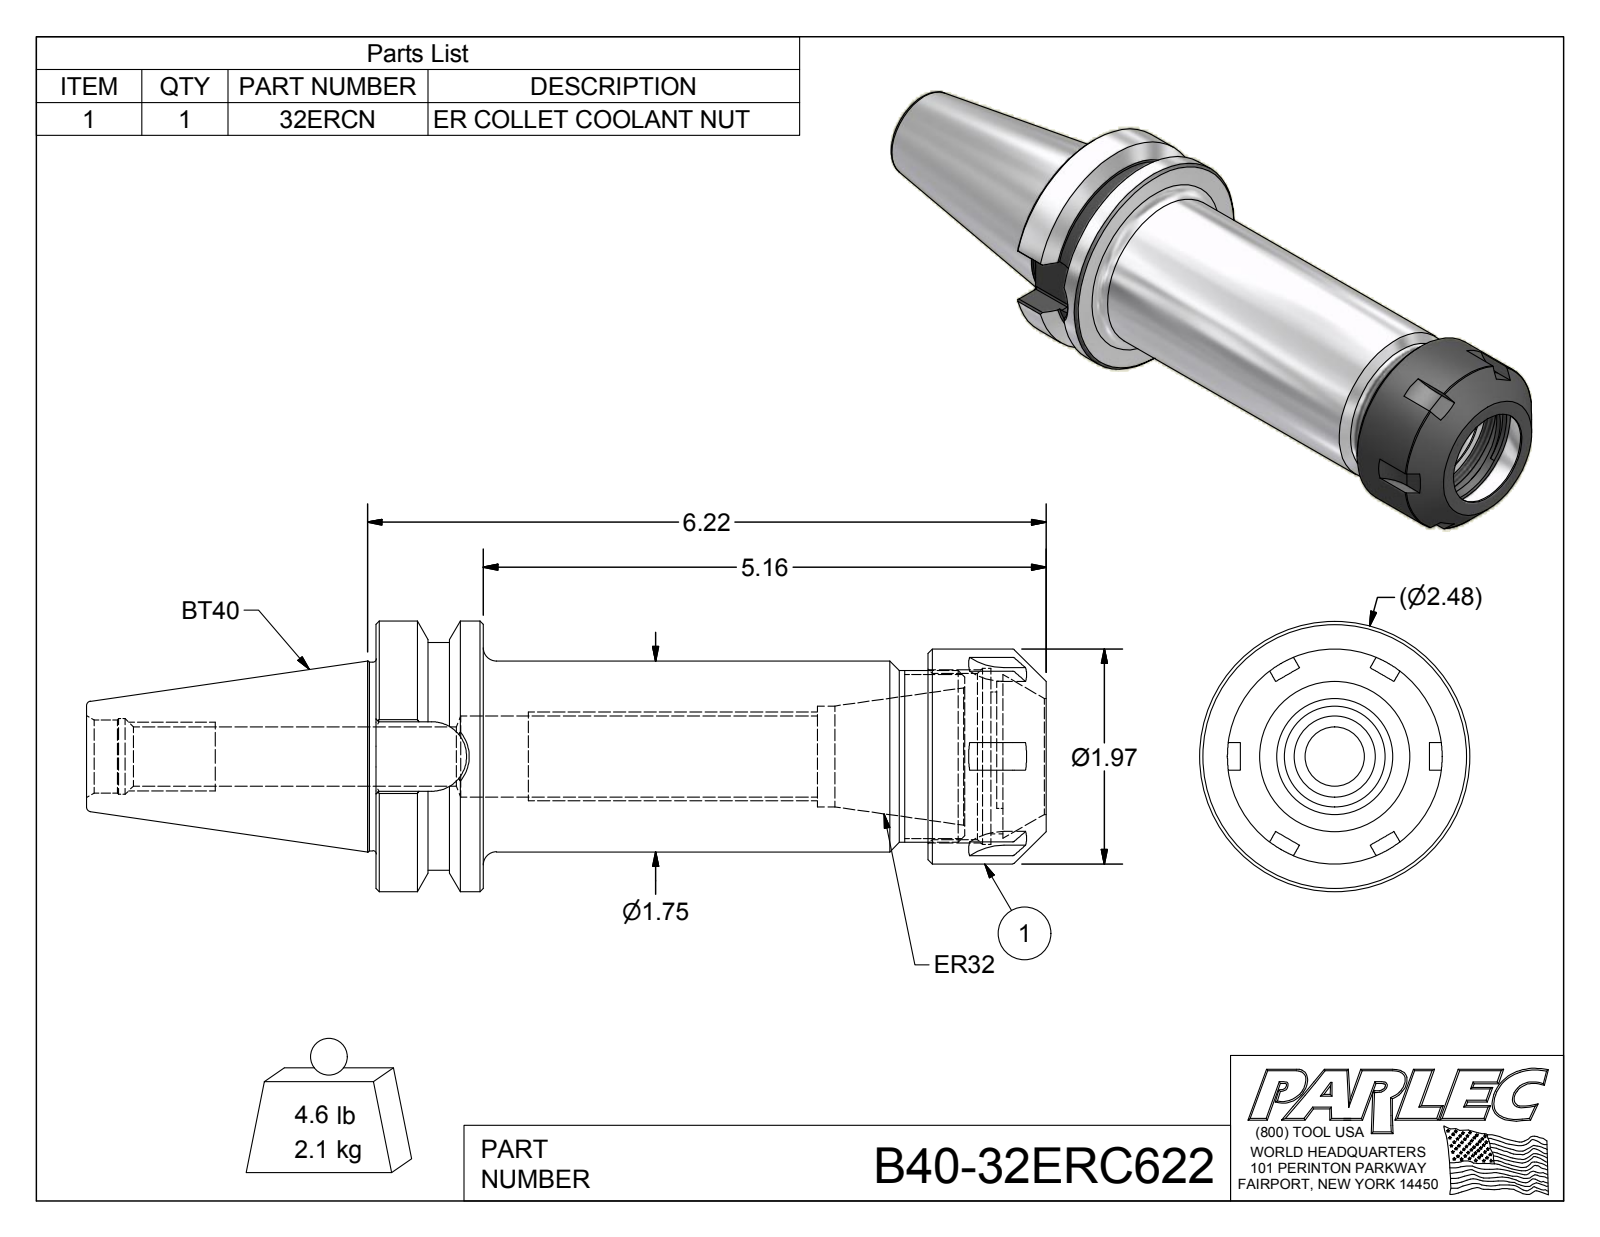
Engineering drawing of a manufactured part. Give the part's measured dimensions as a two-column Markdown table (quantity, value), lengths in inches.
| quantity | value |
| --- | --- |
| part name | B40-32ERC622; B40-32ER6-1; 32ERCN |
| STEP written by | Autodesk Inventor 2012 (AUTOMOTIVE_DESIGN) |
| units | inches |
| bodies | 2 solids, 117 faces (47 planar, 35 cylindrical, 35 other) |
| overall size | 8.795 × 2.48 × 2.48 |
| volume | 16.24 in³ |
| surface area | 84.37 in² |
| round holes (diameter × count) | 0.545 × 1, 0.67 × 1, 0.694 × 1, 0.745 × 1, 0.925 × 1, 1.063 × 1, 1.299 × 1, 1.522 × 1, 1.614 × 1 |
| round bosses / shafts (diameter × count) | 2.48 × 1, 2.087 × 1, 1.969 × 1, 1.75 × 1, 1.73 × 1, 1.575 × 1 |
| partial cylindrical surfaces (radius × count) | 0.02 × 8, 0.5 × 6, 0.319 × 1, 0.689 × 1 |
| main face-to-face distances | 0.984, 5.059, 4.076, 5.638, 4.654, 0.579, 6.142, 5.158, 1.083, 0.504 |
| hole center spacings | 0.059 |
